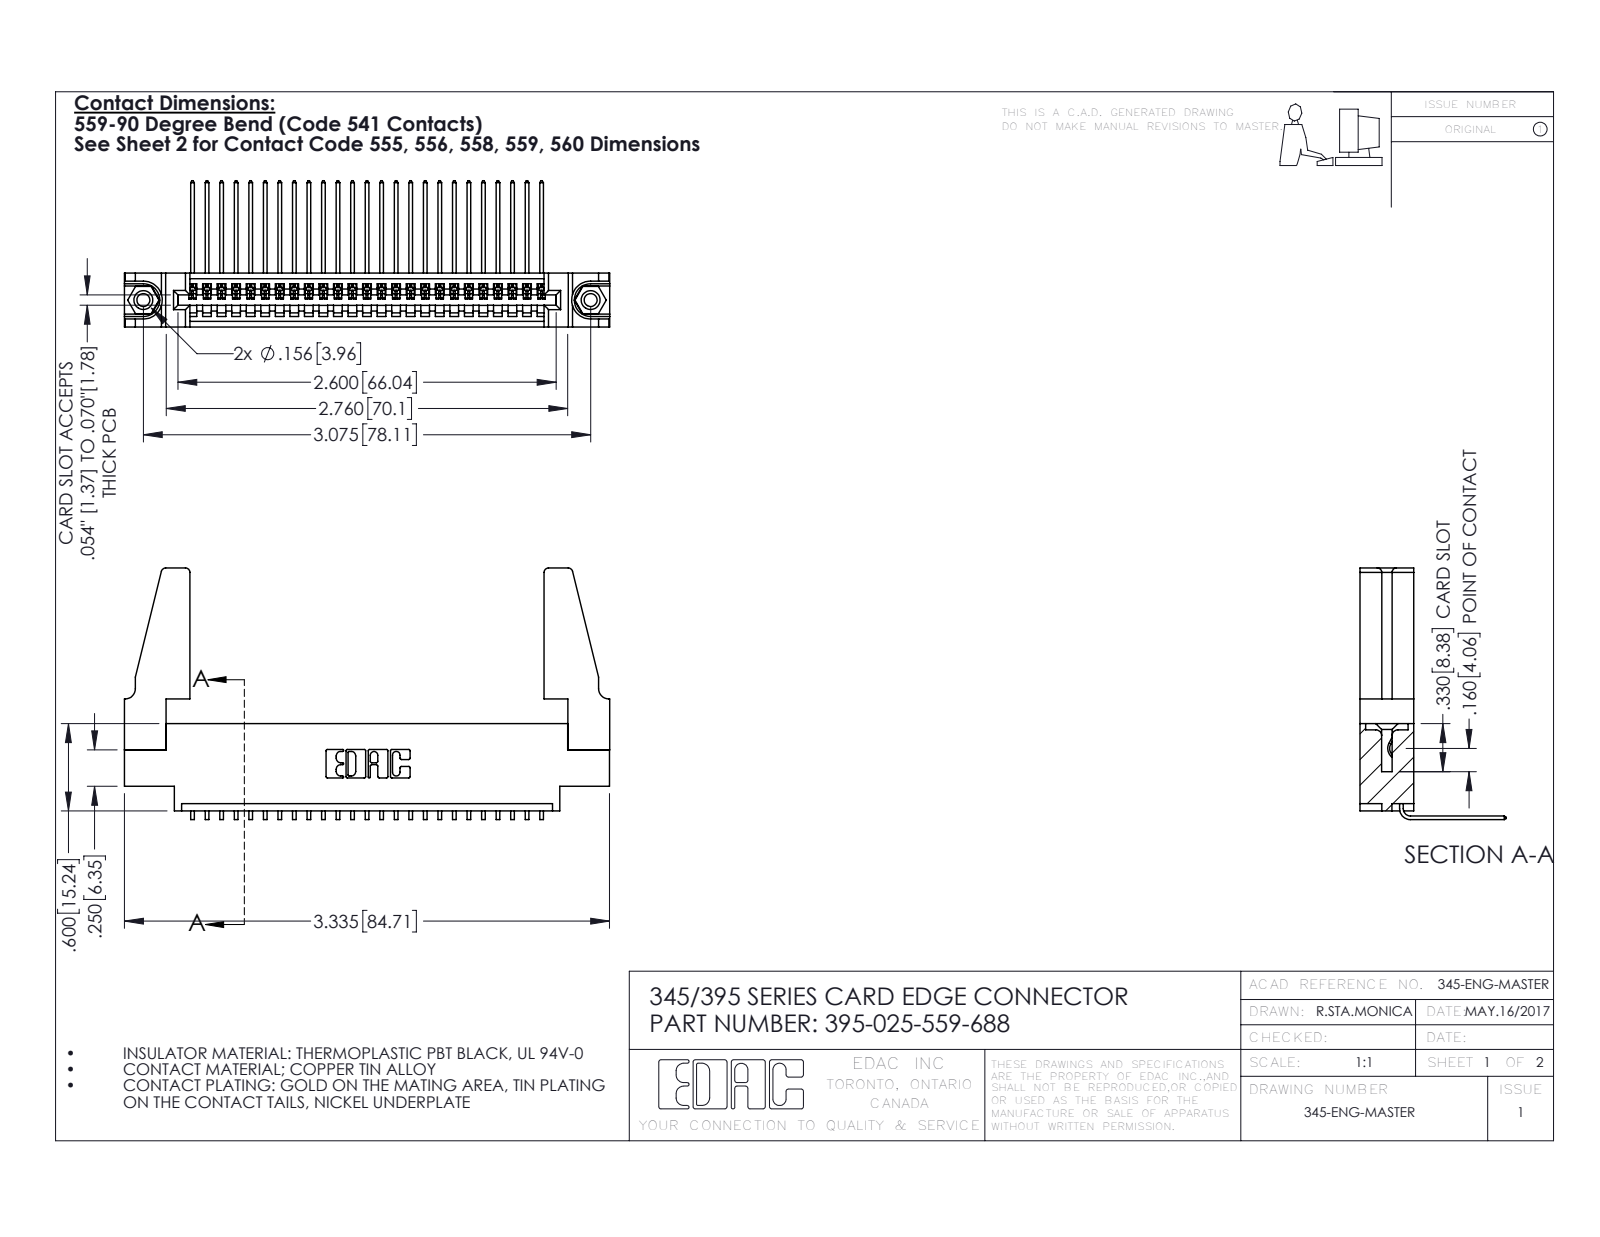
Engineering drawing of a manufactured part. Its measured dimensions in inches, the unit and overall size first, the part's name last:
Units: inches
Overall size (bounding box): 3.336 × 1.729 × 1.005
Round holes (diameter × count): ⌀0.089 ×2, ⌀0.125 ×2, ⌀0.156 ×2, ⌀0.064 ×1
Round bosses / shafts (diameter × count): ⌀0.155 ×2
Partial cylindrical surfaces — rounded edges, fillets, slot ends (radius × count): R0.006 ×50, R0.01 ×22, R0.03 ×8, R0.007 ×6, R0.031 ×6, R0.026 ×3, R0.031 ×2, R0.04 ×2
Main face-to-face distances: 0.37, 0.072, 0.298, 0.2, 0.098, 0.272, 0.025, 0.225, 0.175, 0.149
Hole centre spacings: 0.27, 2.84, 3.075
Volume: 0.679 in³ · Surface area: 21.68 in²
Bodies: 30 solids, 1754 faces (1206 planar, 532 cylindrical, 16 other)
Part name (STEP PRODUCT): 345-292-001_558 559 Tail - 1; 345 Part_0.170 Offset - 0.156 Dia-TH; 345-220-078_345-220-088; 395-025-559-688 (+1 more)
STEP written by: SolidWorks 2016 (CONFIG_CONTROL_DESIGN)
